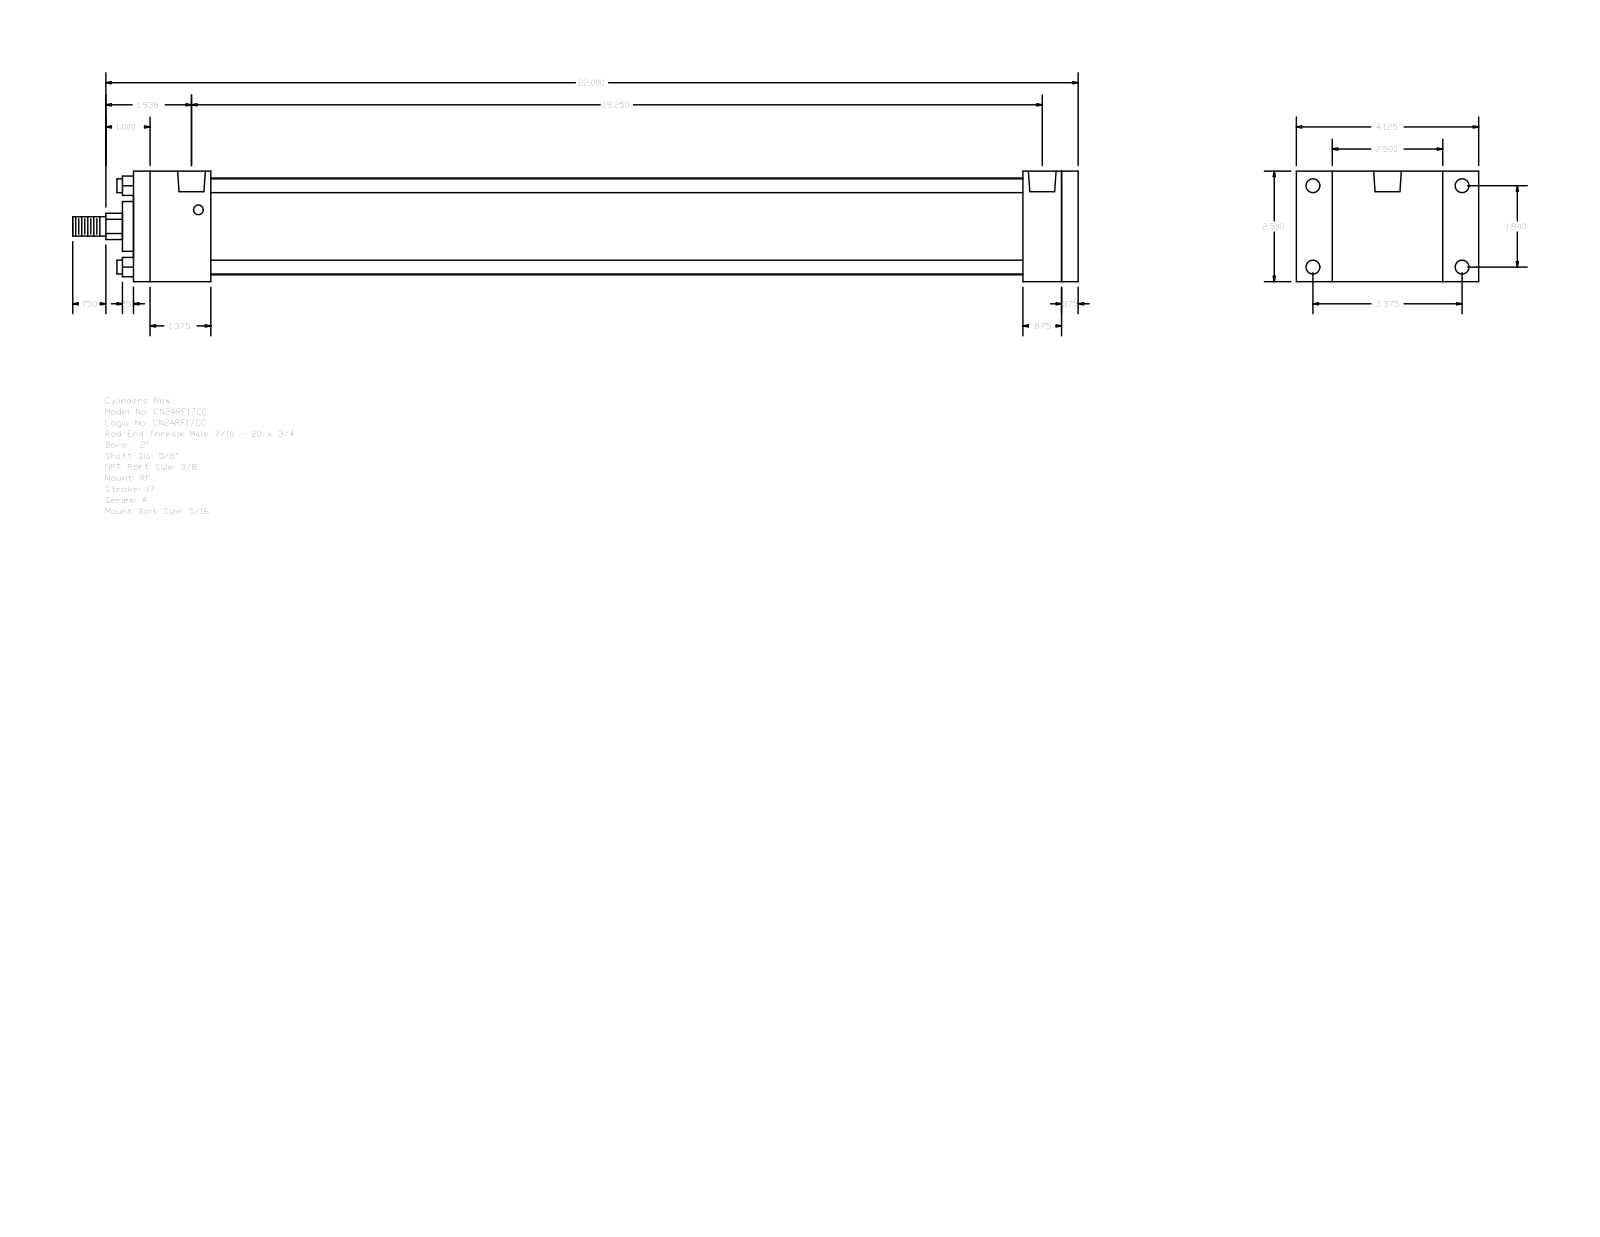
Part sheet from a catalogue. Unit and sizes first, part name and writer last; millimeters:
Units: millimetres
Overall size (bounding box): 577.85 × 104.78 × 63.5
Round holes (diameter × count): ⌀5.56 ×4, ⌀7.94 ×4, ⌀15.93 ×2
Round bosses / shafts (diameter × count): ⌀7.94 ×4, ⌀55.63 ×1, ⌀28.57 ×1, ⌀15.88 ×1, ⌀11.11 ×1
Partial cylindrical surfaces — rounded edges, fillets, slot ends (radius × count): R7.54 ×1
Main face-to-face distances: 63.5, 542.92, 9.53, 533.39, 44.45, 488.94, 498.47, 511.17, 466.72, 22.22
Hole centre spacings: 46.74, 85.72, 97.63, 481, 3.97, 3.98, 484.97, 484.98
Bodies: 0 solids, 92 faces (64 planar, 28 cylindrical, 0 other)
Part name (STEP PRODUCT): A_RF__0200_0.625
STEP written by: GSSL Pune (CONFIG_CONTROL_DESIGN)
